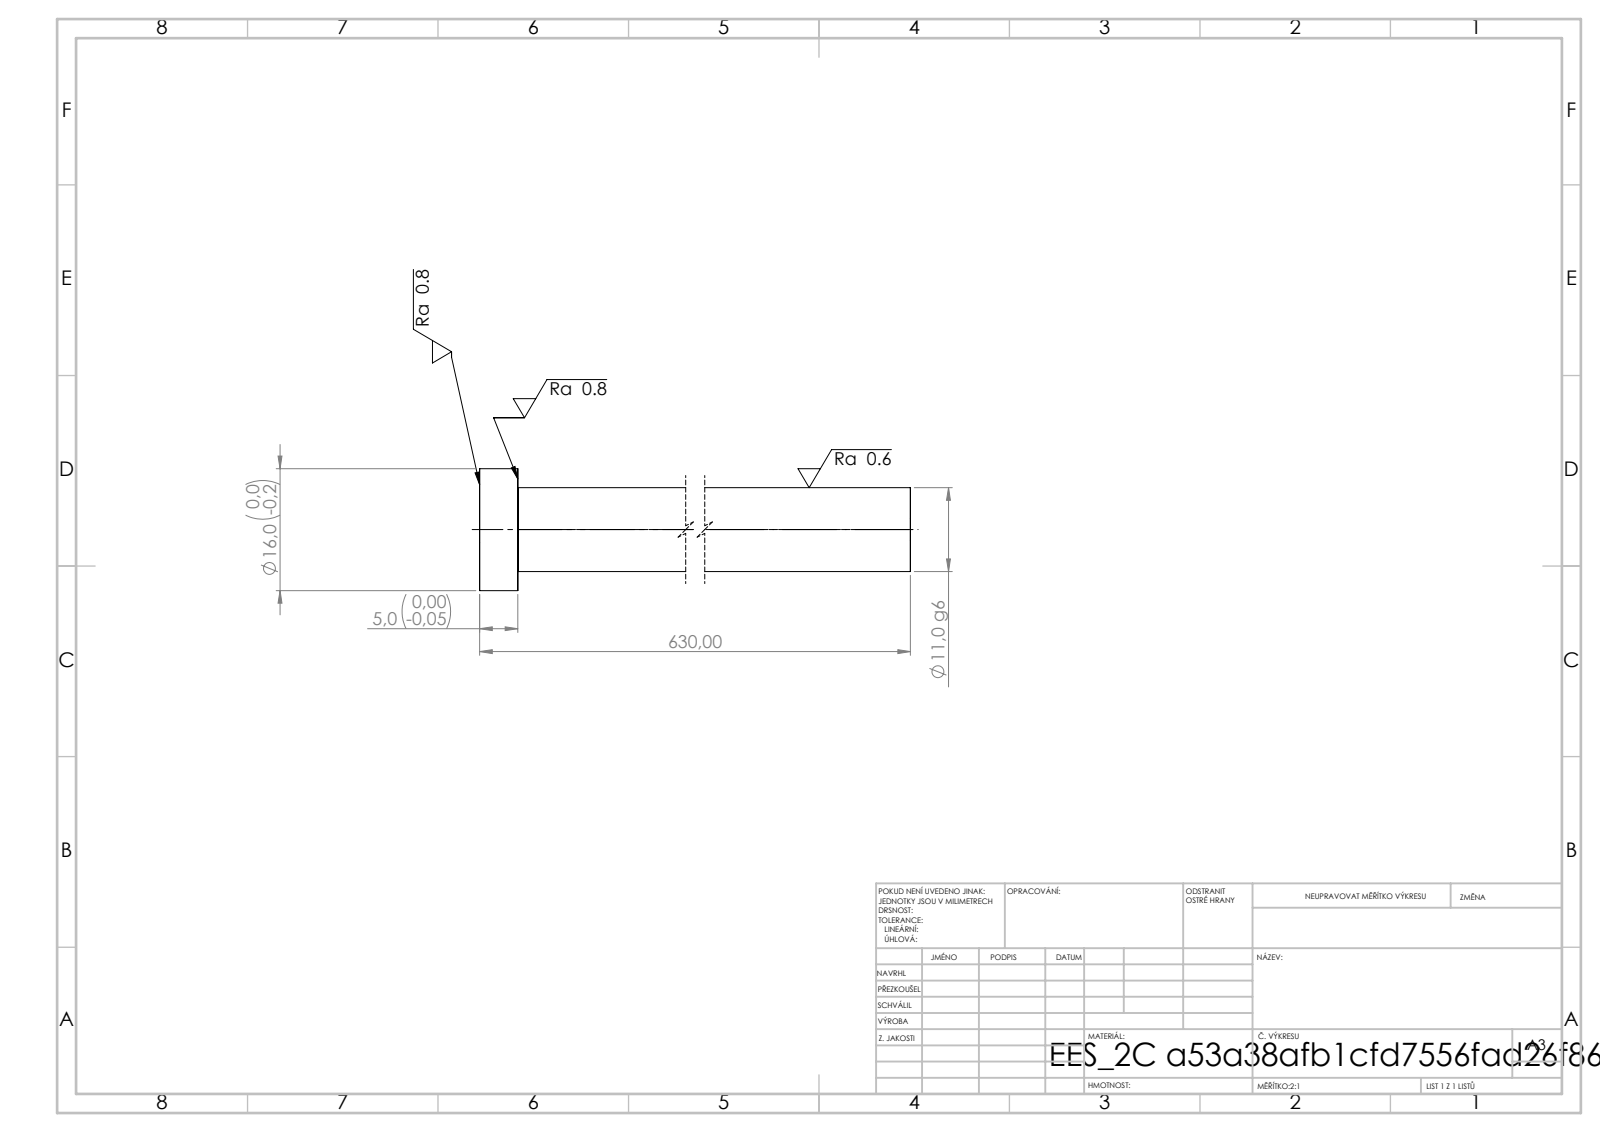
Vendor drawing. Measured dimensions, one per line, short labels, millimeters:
written by: SolidWorks 2019 (CONFIG_CONTROL_DESIGN)
unit: mm
bodies: 1 solid, 7 faces (3 planar, 4 cylindrical, 0 other)
size: 630 × 16 × 16
volume: 60 401 mm³; area: 22 252 mm²
bosses: 1× ⌀16, 1× ⌀11
face distances: 5, 630, 625
